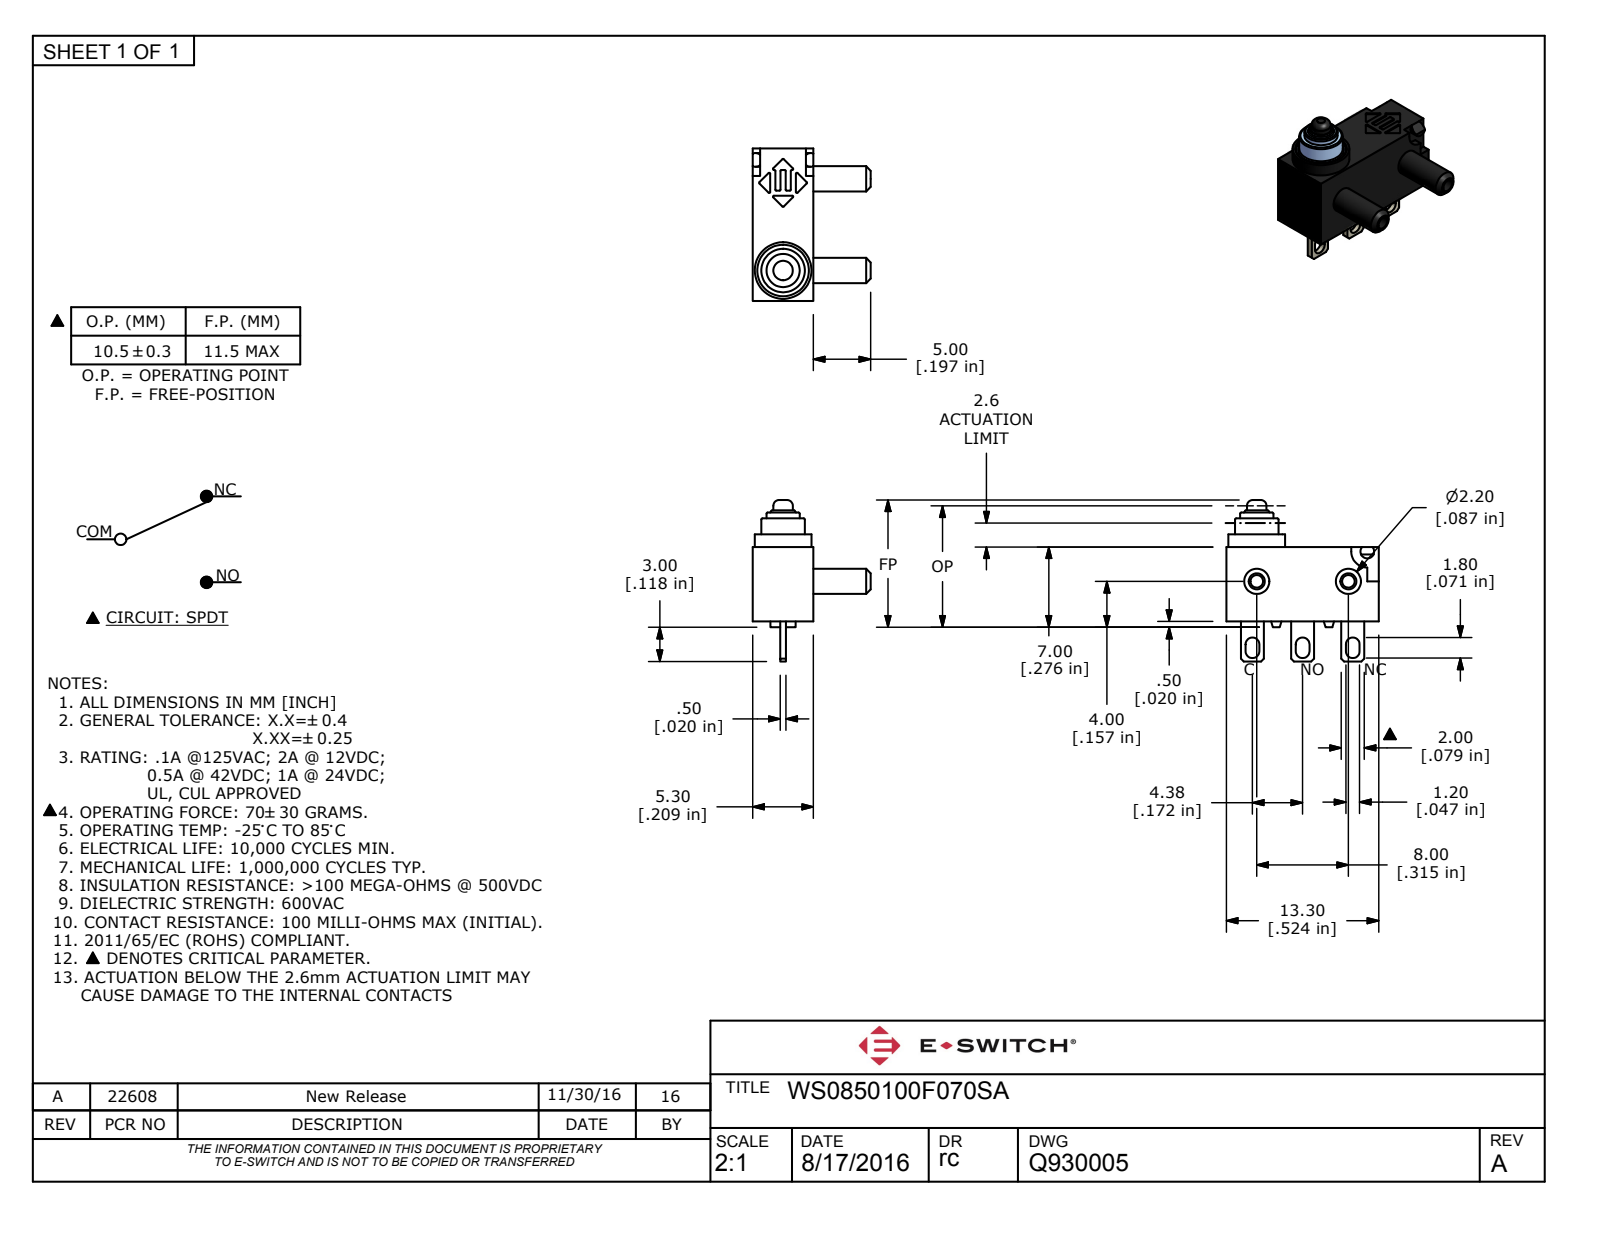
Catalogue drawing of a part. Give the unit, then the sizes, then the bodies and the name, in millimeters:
Units: millimetres
Overall size (bounding box): 14.1 × 13.3 × 10.3
Round holes (diameter × count): ⌀1.1 ×2, ⌀4.5 ×1
Round bosses / shafts (diameter × count): ⌀2.2 ×2, ⌀5 ×1, ⌀3.8 ×1, ⌀2.9 ×1, ⌀1.7 ×1
Partial cylindrical surfaces — rounded edges, fillets, slot ends (radius × count): R0.6 ×7, R1.4 ×1
Main face-to-face distances: 5.3, 6.5, 2.9, 2.4, 13.3, 0.5, 6.4, 4.6, 0.7, 1.8
Hole centre spacings: 8
Volume: 520 mm³ · Surface area: 594 mm²
Bodies: 1 solid, 147 faces (99 planar, 39 cylindrical, 9 other)
Part name (STEP PRODUCT): P:\\E-Switch Secure\\3D_MODELS_STP_FORMAT\\WS0850100F070SA.stp
STEP written by: ACIS (CONFIG_CONTROL_DESIGN)
